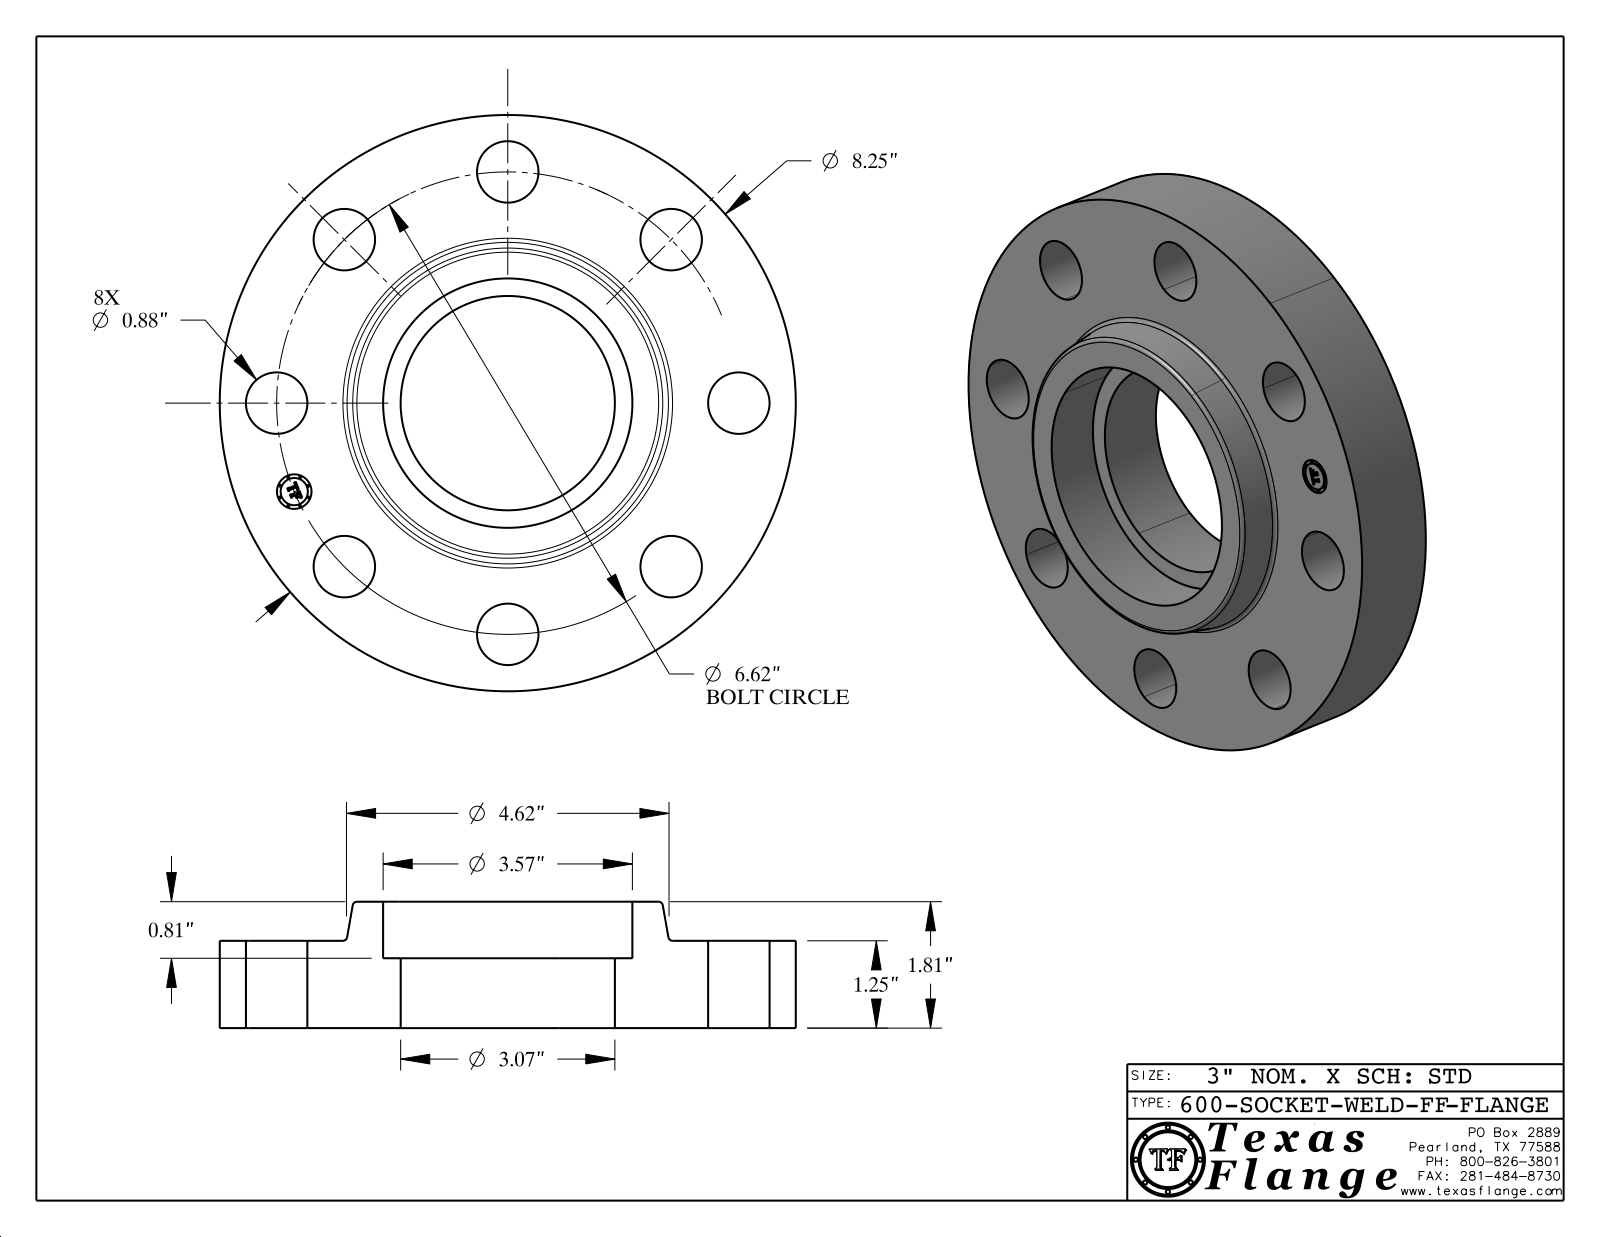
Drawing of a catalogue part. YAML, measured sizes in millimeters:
part_name: "600-SOCKET-WELD-FF"
step_written_by: "CATIA V5 STEP AP214 (AUTOMOTIVE_DESIGN)"
units: millimeters
bodies: {solids: 1, faces: 417, planar: 369, cylindrical: 42, other: 6}
overall_size: [209.6, 209.6, 46]
volume: 888700
surface_area: 108000
round_holes:
  - {diameter: 22.4, count: 8}
  - {diameter: 12.6, count: 1}
  - {diameter: 77.9, count: 1}
  - {diameter: 90.7, count: 1}
round_bosses_or_shafts:
  - {diameter: 0.8, count: 8}
  - {diameter: 209.6, count: 1}
  - {diameter: 9.9, count: 1}
face_to_face_distances: [31.8, 46, 14.2, 25.4, 6.4, 20.6, 0.4, 31.4, 6, 14.6]
hole_center_spacings: [84.1, 64.3, 155.3, 118.9, 118.9, 32.8, 93.4, 164.9]
